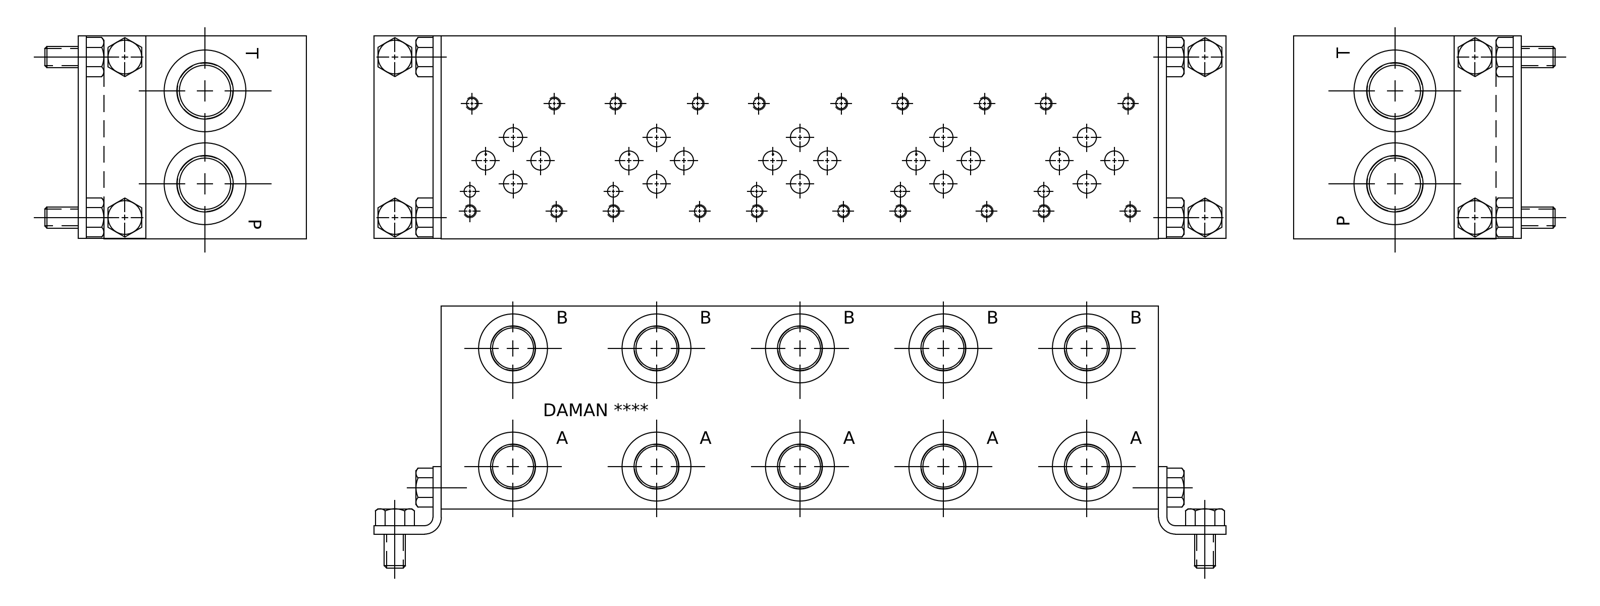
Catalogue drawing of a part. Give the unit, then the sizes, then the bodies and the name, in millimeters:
Units: millimetres
Overall size (bounding box): 269.88 × 76.2 × 76.2
Round holes (diameter × count): ⌀4.22 ×20, ⌀5 ×20, ⌀7.14 ×15, ⌀14.3 ×10, ⌀15.06 ×10, ⌀16.76 ×10, ⌀25.93 ×10, ⌀3.96 ×5, ⌀6.35 ×5, ⌀6.76 ×2, ⌀8 ×2, ⌀15.88 ×2
Main face-to-face distances: 76.2, 0.79, 269.88, 75.41, 269.09, 268.3, 12.98, 12.19, 63.22, 1
Hole centre spacings: 107.95, 53.98, 53.97, 40.49, 51.45, 161.93, 46.18, 116.74
Volume: 1 475 000 mm³ · Surface area: 120 732 mm²
Bodies: 1 solid, 830 faces (433 planar, 129 cylindrical, 268 other)
Part name (STEP PRODUCT): Part_AD03P052B_3D
STEP written by: Autodesk Inventor 2019 (AUTOMOTIVE_DESIGN)
